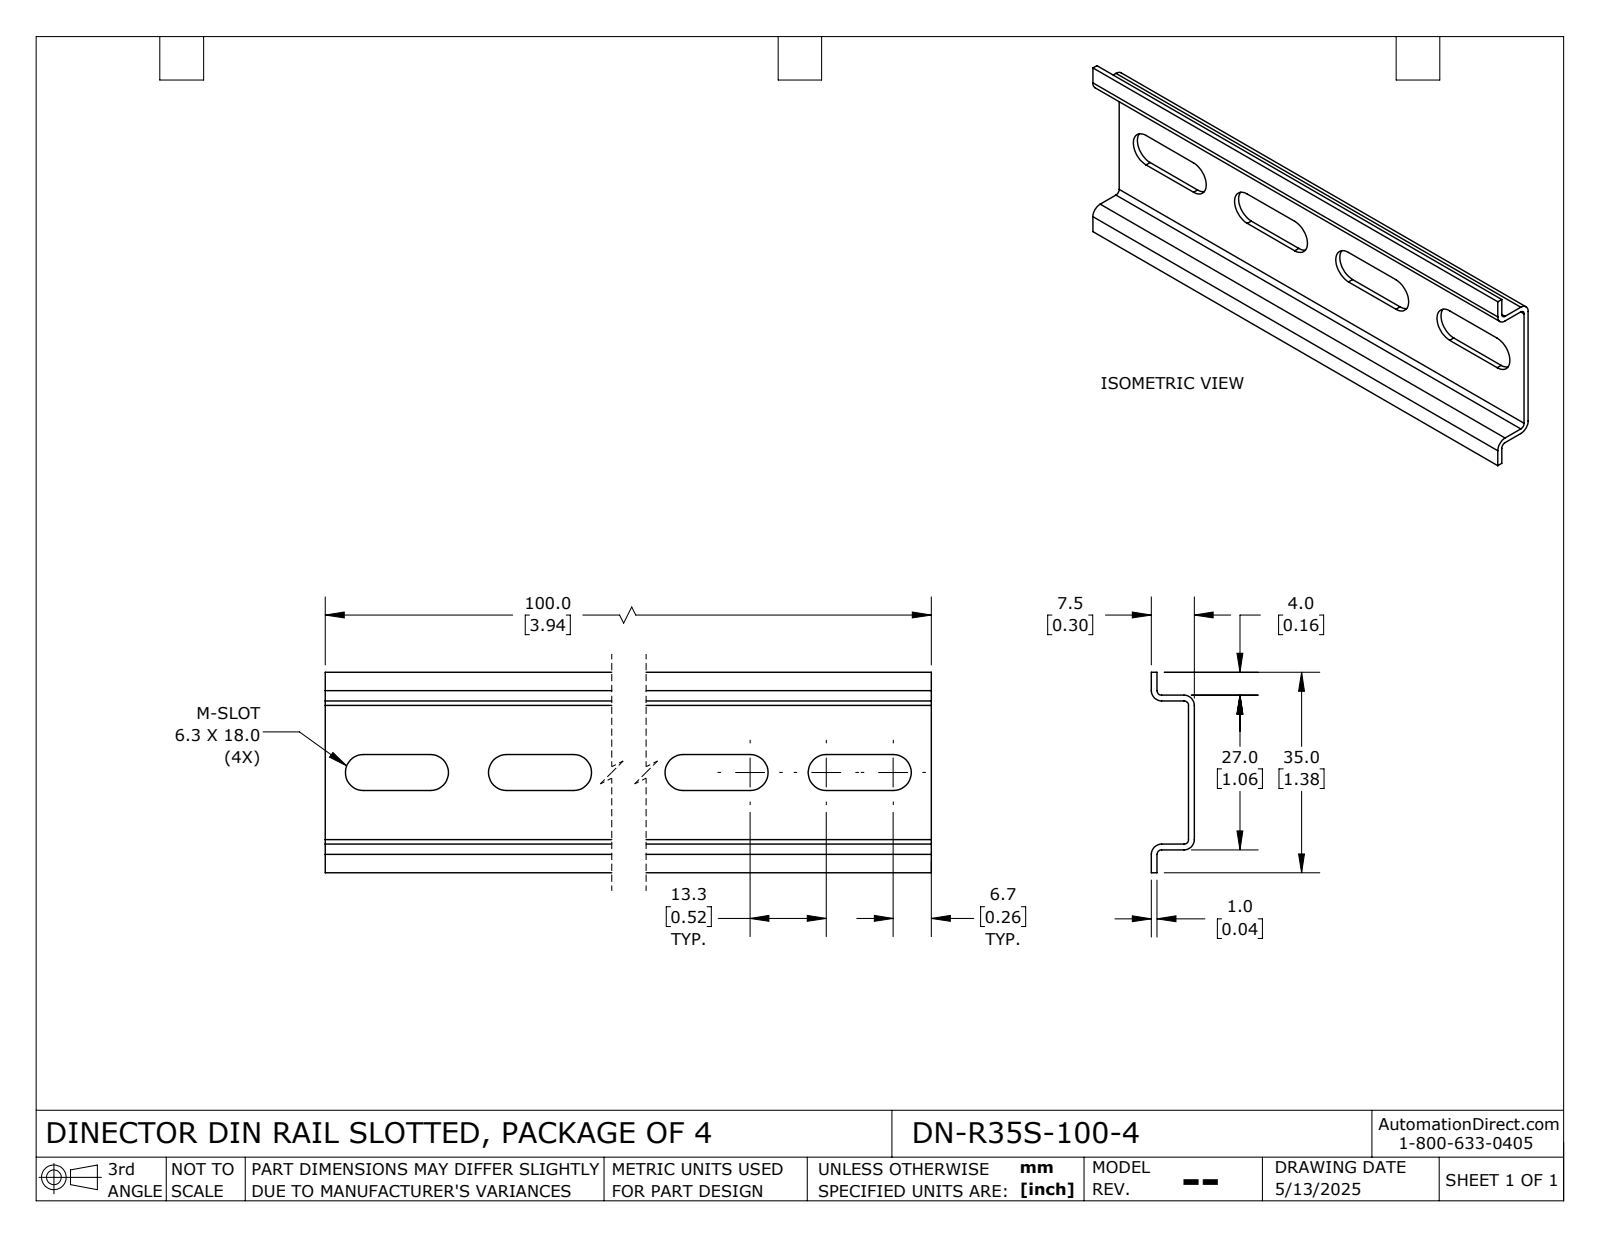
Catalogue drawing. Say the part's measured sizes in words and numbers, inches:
The part is named "DN-R35S-100-4_Default". Its 3-D file was written by "SolidWorks 2024 (CONFIG_CONTROL_DESIGN)". It is 1 solid with 38 faces: 22 planar, 16 cylindrical and 0 other. Overall it measures 3.937 by 1.378 by 0.295 inches. Its volume is 0.254 cubic inches and its surface area 13.61 square inches. Partial cylindrical surfaces (rounded edges, fillets, slot ends): 8 of radius 0.124, 4 of radius 0.031, 4 of radius 0.071. The main face-to-face distances are 0.039, 0.256, 1.024, 0.295, 0.217, 1.063, 0.984, 0.157, 0.197, 1.181.
